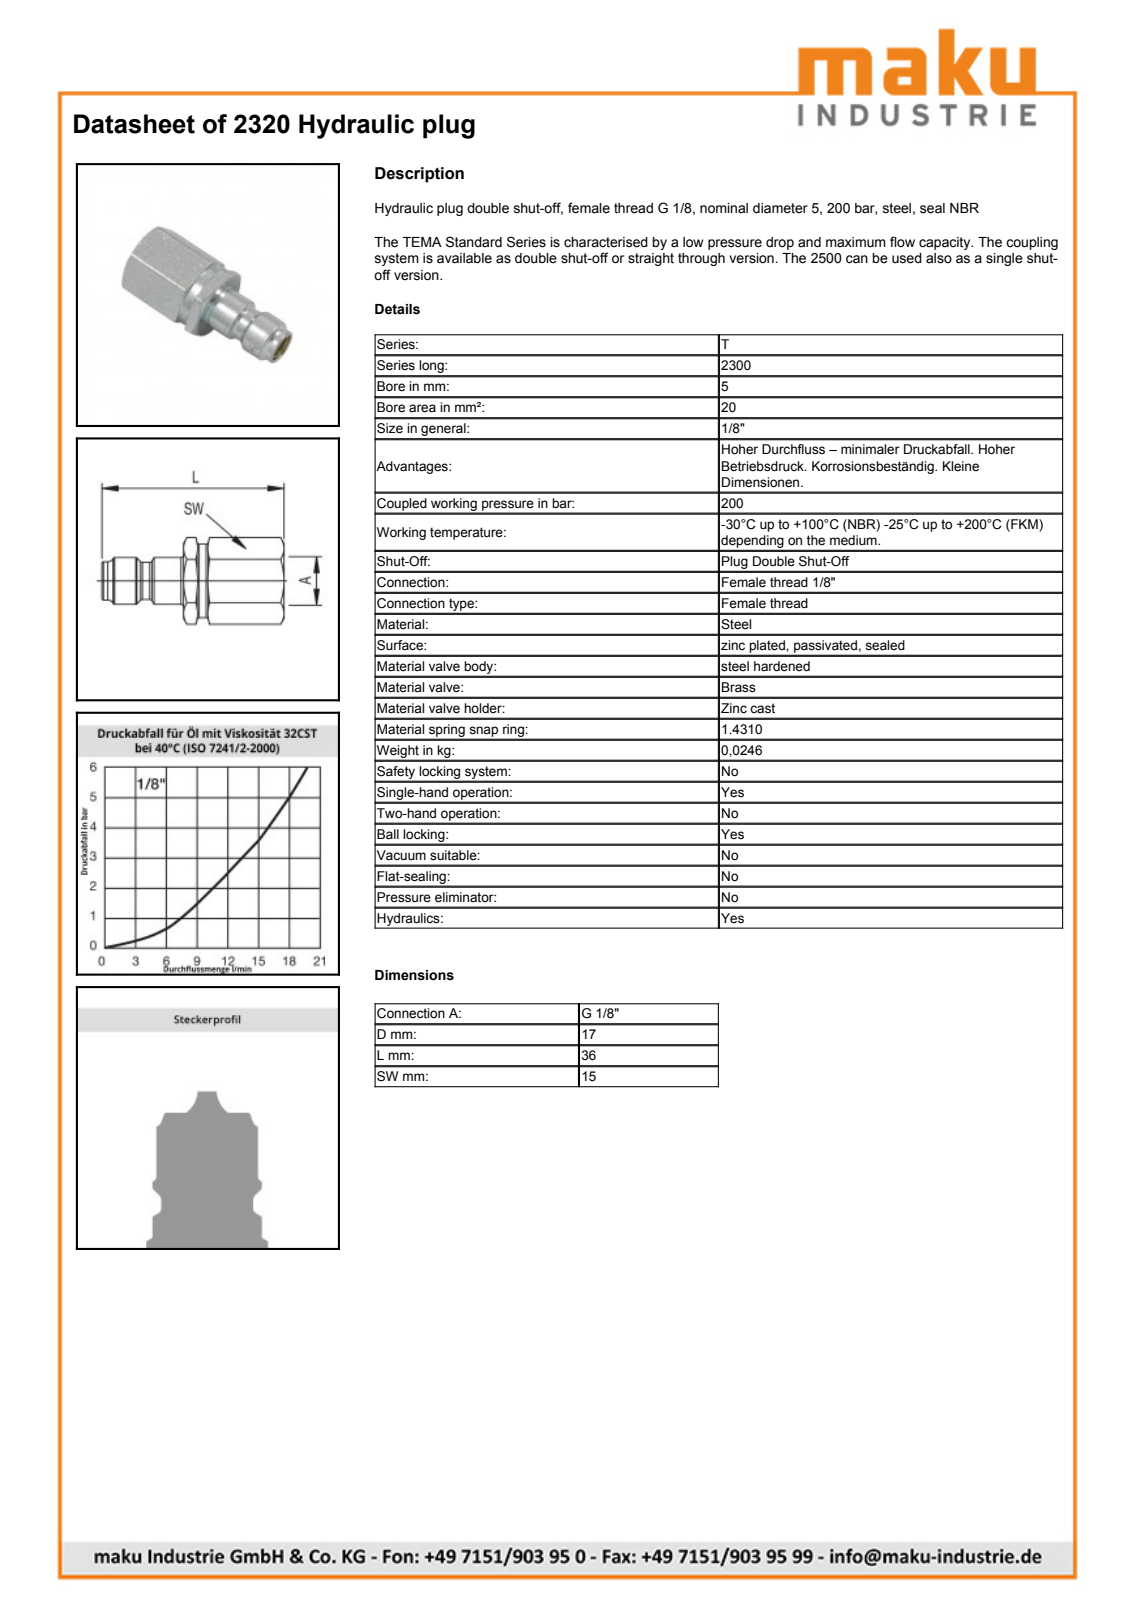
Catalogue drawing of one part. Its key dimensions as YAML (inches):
part_name: "2320"
step_written_by: "SolidWorks 2009 (AUTOMOTIVE_DESIGN)"
units: inches
bodies: {solids: 1, faces: 77, planar: 17, cylindrical: 18, other: 42}
overall_size: [1.423, 0.682, 0.591]
volume: 0.242
surface_area: 3.753
round_holes:
  - {diameter: 0.185, count: 1}
  - {diameter: 0.228, count: 1}
  - {diameter: 0.343, count: 1}
round_bosses_or_shafts:
  - {diameter: 0.579, count: 1}
  - {diameter: 0.376, count: 1}
  - {diameter: 0.307, count: 1}
  - {diameter: 0.283, count: 1}
  - {diameter: 0.224, count: 1}
face_to_face_distances: [0.591, 0.785, 0.39, 0.396, 0.638, 1.028, 1.423, 0.018, 0.62, 1.01]
